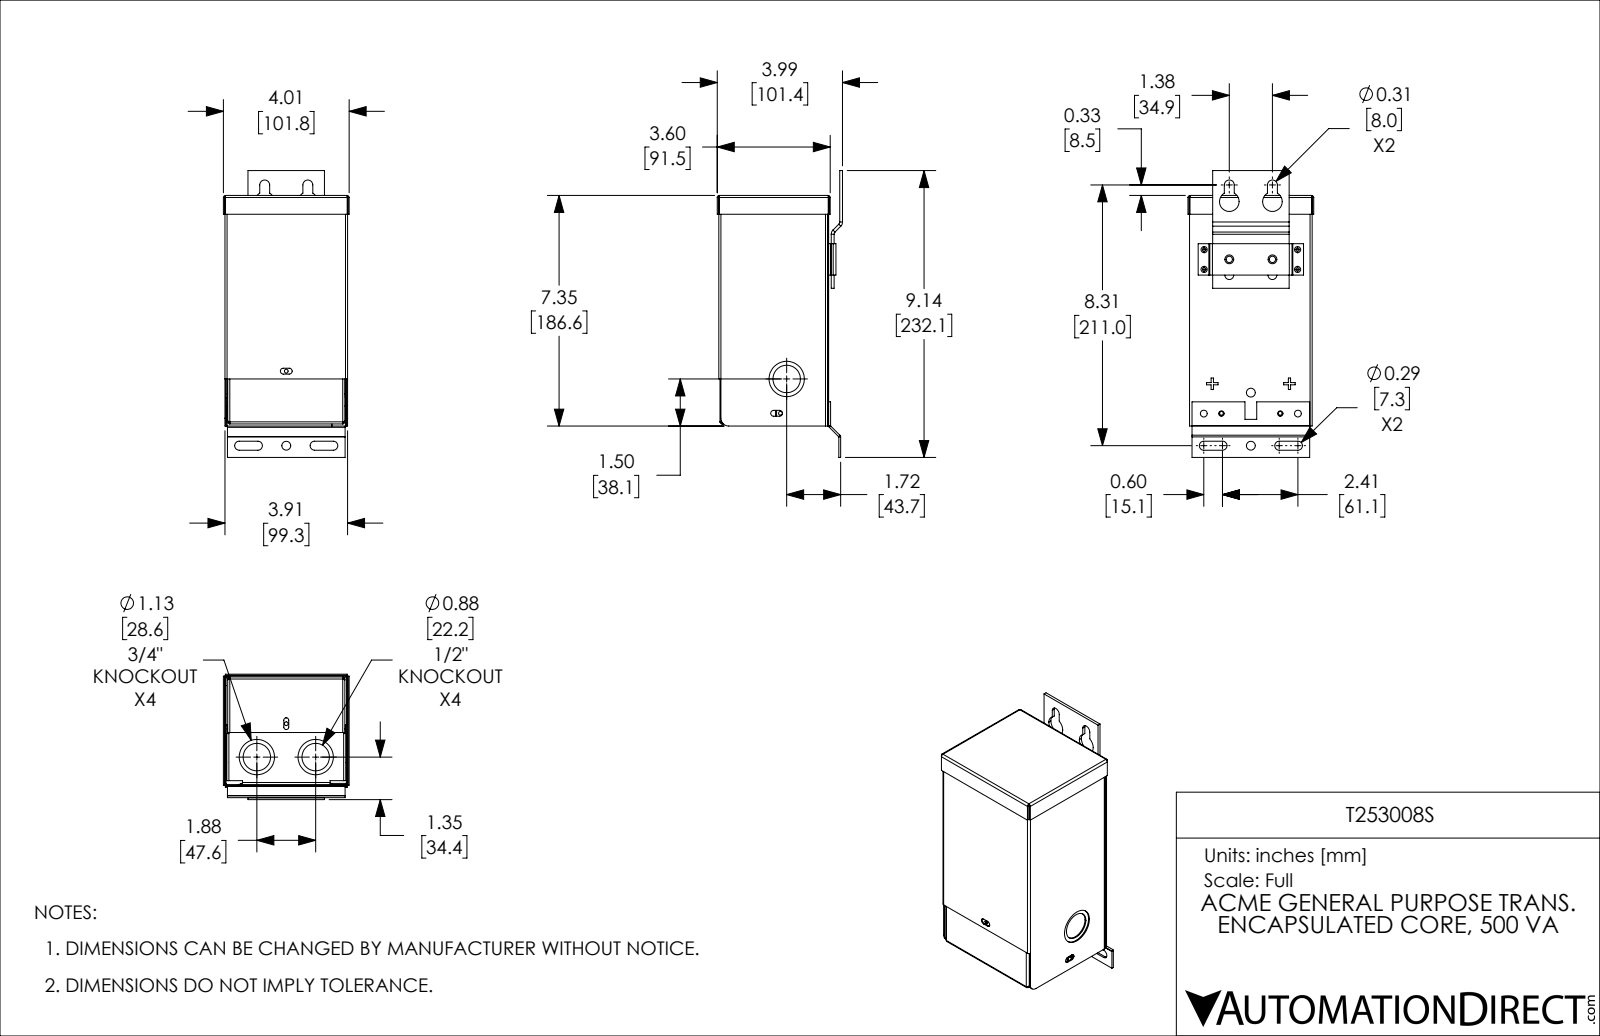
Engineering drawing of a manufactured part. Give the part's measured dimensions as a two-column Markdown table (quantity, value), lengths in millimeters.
| quantity | value |
| --- | --- |
| part name | T253008S |
| STEP written by | SolidWorks 2021 (CONFIG_CONTROL_DESIGN) |
| units | millimeters |
| bodies | 7 solids, 528 faces (326 planar, 154 cylindrical, 48 other) |
| overall size | 232.07 × 101.8 × 101.43 |
| volume | 113 073 mm³ |
| surface area | 227 401 mm² |
| round holes (diameter × count) | 3.05 × 5, 7.14 × 3, 7.14 × 3, 22.22 × 3, 28.57 × 3, 4.34 × 2, 4.76 × 2, 5.11 × 2, 5.54 × 2, 15.88 × 2, 28.58 × 1 |
| round bosses / shafts (diameter × count) | 30.4 × 3, 24.05 × 3 |
| partial cylindrical surfaces (radius × count) | 0.79 × 16, 1.7 × 16, 2.38 × 8, 0.66 × 4, 2.18 × 4, 3.66 × 4, 0.43 × 2, 1.96 × 2 |
| main face-to-face distances | 0.91, 87.99, 98.41, 87.08, 99.32, 97.5, 88.9, 1.53, 183.95, 182.42 |
| hole center spacings | 34.92, 12.7, 12.74, 14.27, 14.29, 29.09, 29.23, 34.94 |
